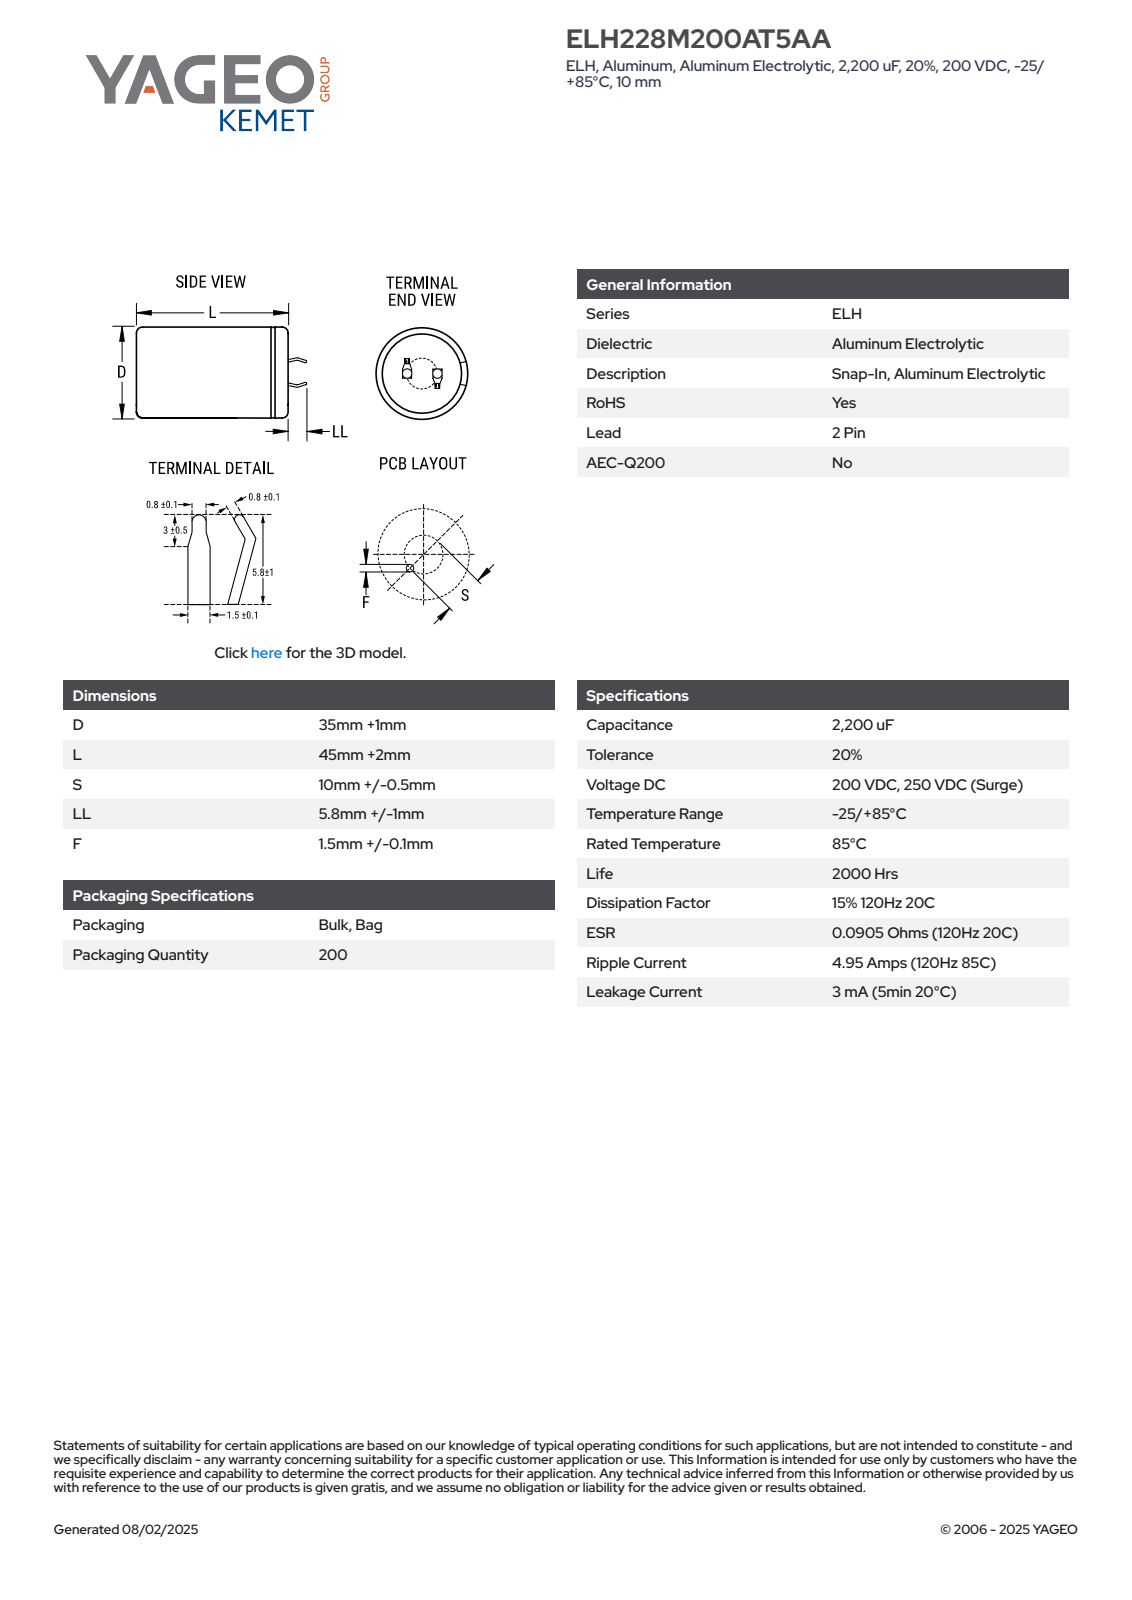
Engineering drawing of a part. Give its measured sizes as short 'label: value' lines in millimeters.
name: CARS_K2P_35X45_D36L47S10LL6.8F1.6
written by: SolidWorks 2014 (AUTOMOTIVE_DESIGN)
unit: mm
bodies: 1 solid, 100 faces (52 planar, 9 cylindrical, 39 other)
size: 53.79 × 36 × 36
volume: 47 312 mm³; area: 7 346 mm²
holes: 1× ⌀31.85
bosses: 1× ⌀36
rounds: 1× R17.99
face distances: 46.99, 47.49, 0.5, 0.6, 7.08, 0.75, 1.35, 7.68, 6.48, 0.59
